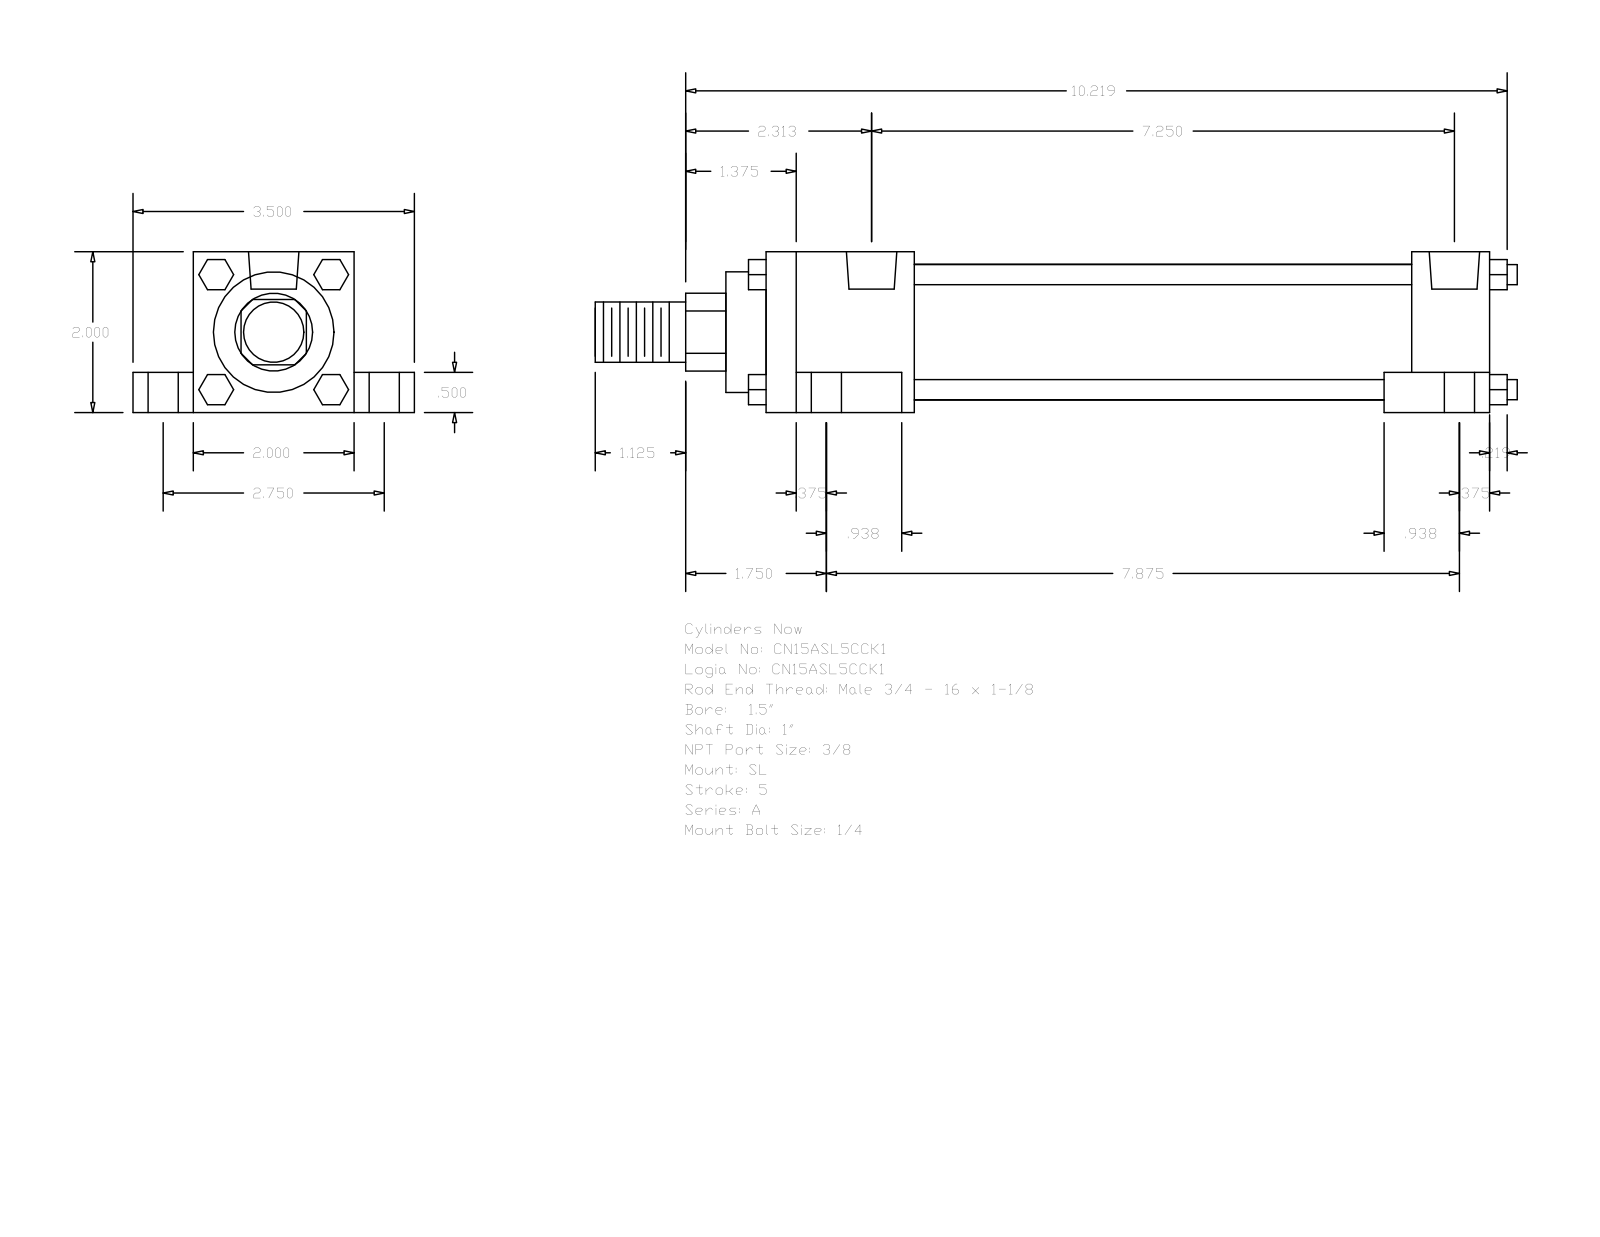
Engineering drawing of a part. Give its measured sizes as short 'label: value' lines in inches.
name: A_SL__0150_1
written by: GSSL Pune (CONFIG_CONTROL_DESIGN)
unit: in
bodies: 0 solids, 148 faces (112 planar, 36 cylindrical, 0 other)
size: 11.469 × 3.5 × 2
holes: 4× ⌀0.219, 4× ⌀0.375, 4× ⌀0.625, 2× ⌀0.627
bosses: 4× ⌀0.25, 1× ⌀1.69, 1× ⌀1.5, 1× ⌀1, 1× ⌀0.75
rounds: 1× R0.484
face distances: 2, 0.5, 1.5, 0.75, 2.75, 0.375, 9, 1.313, 8.031, 0.969
hole spacings: 0.156, 1.376, 1.392, 1.485, 1.552, 2.75, 6.937, 7.094
